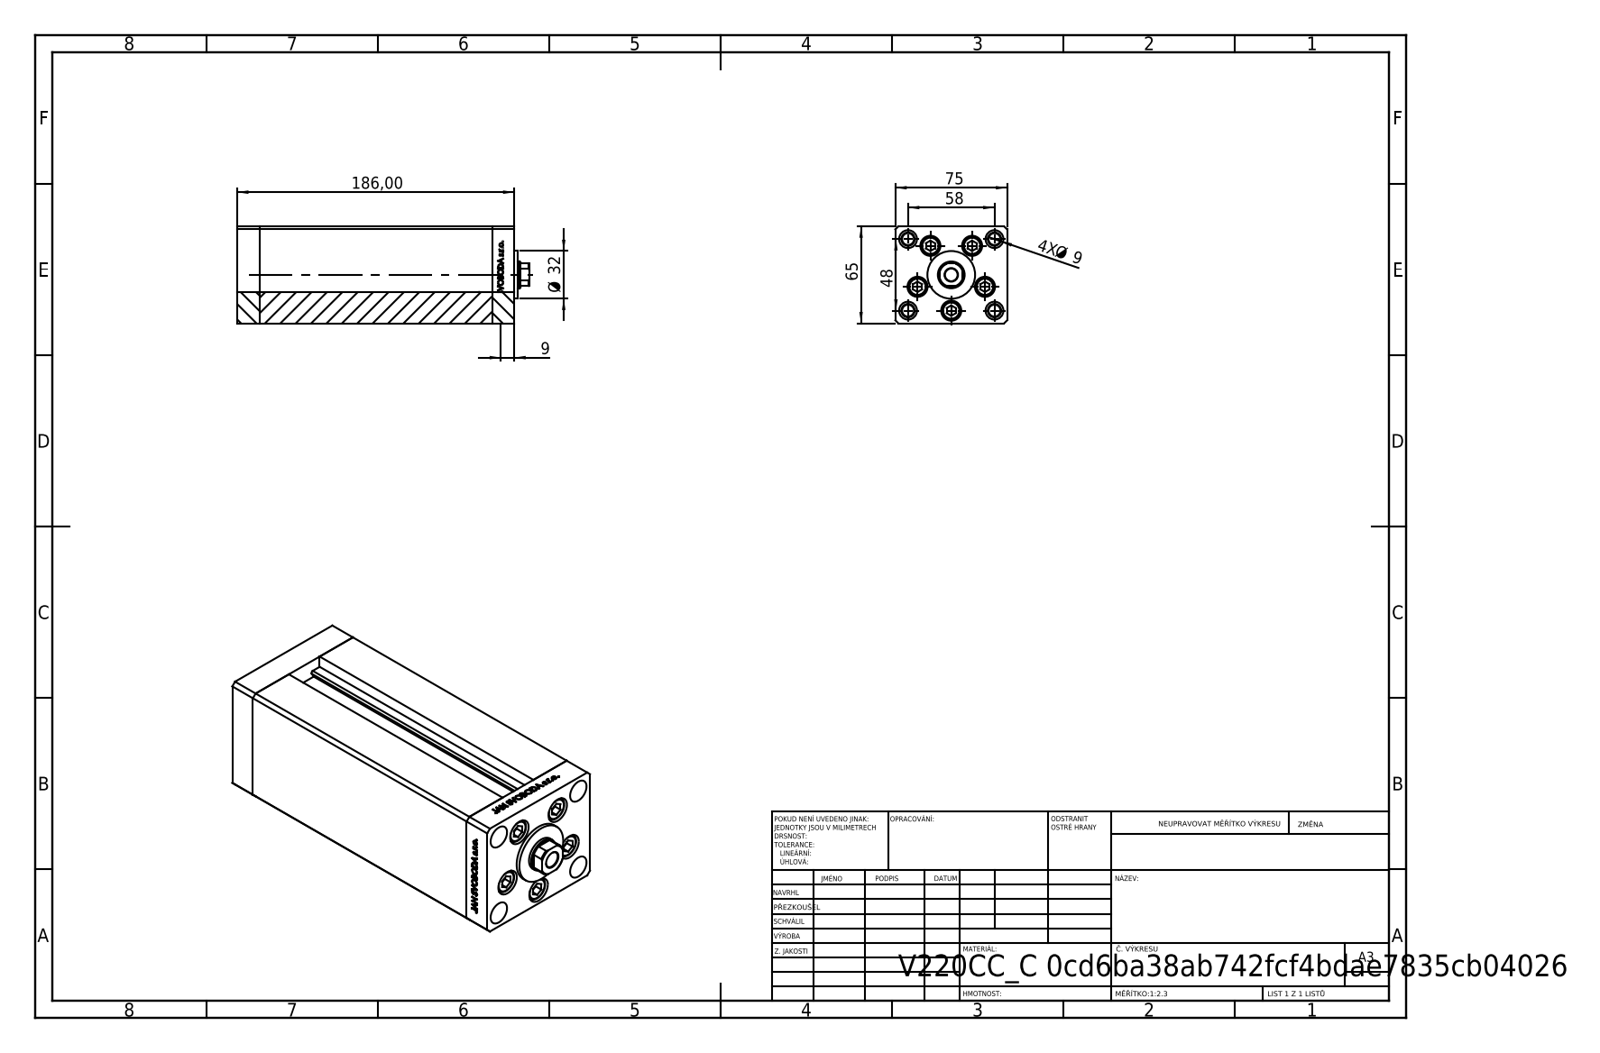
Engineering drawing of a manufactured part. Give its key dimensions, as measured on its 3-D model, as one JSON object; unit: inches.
{"part_name": "V220C FRONT; ALLEN BOLT; V220C BACK_C; V220C_C MIDDLE (+1 more)", "step_written_by": "SolidWorks 2019 (CONFIG_CONTROL_DESIGN)", "units": "inches", "bodies": {"solids": 13, "faces": 1159, "planar": 538, "cylindrical": 159, "other": 462}, "overall_size": [7.717, 2.953, 2.559], "volume_in3": 46.47, "surface_area_in2": 236.7, "round_holes": [[0.354, 9], [0.531, 5], [0.315, 4], [0.472, 4], [0.335, 1], [0.492, 1], [0.709, 1]], "round_bosses_or_shafts": [[0.315, 5], [0.492, 4], [1.26, 1]], "partial_cylinders_radius": [[0.037, 2], [0.335, 1]], "face_to_face_distances": [2.953, 2.559, 0.591, 6.142, 6.732, 7.323, 1.102, 2.146, 0.413, 1.033], "hole_center_spacings": [0.945, 1.482, 0.617, 0.678, 1.091, 1.135, 1.142, 1.285]}
